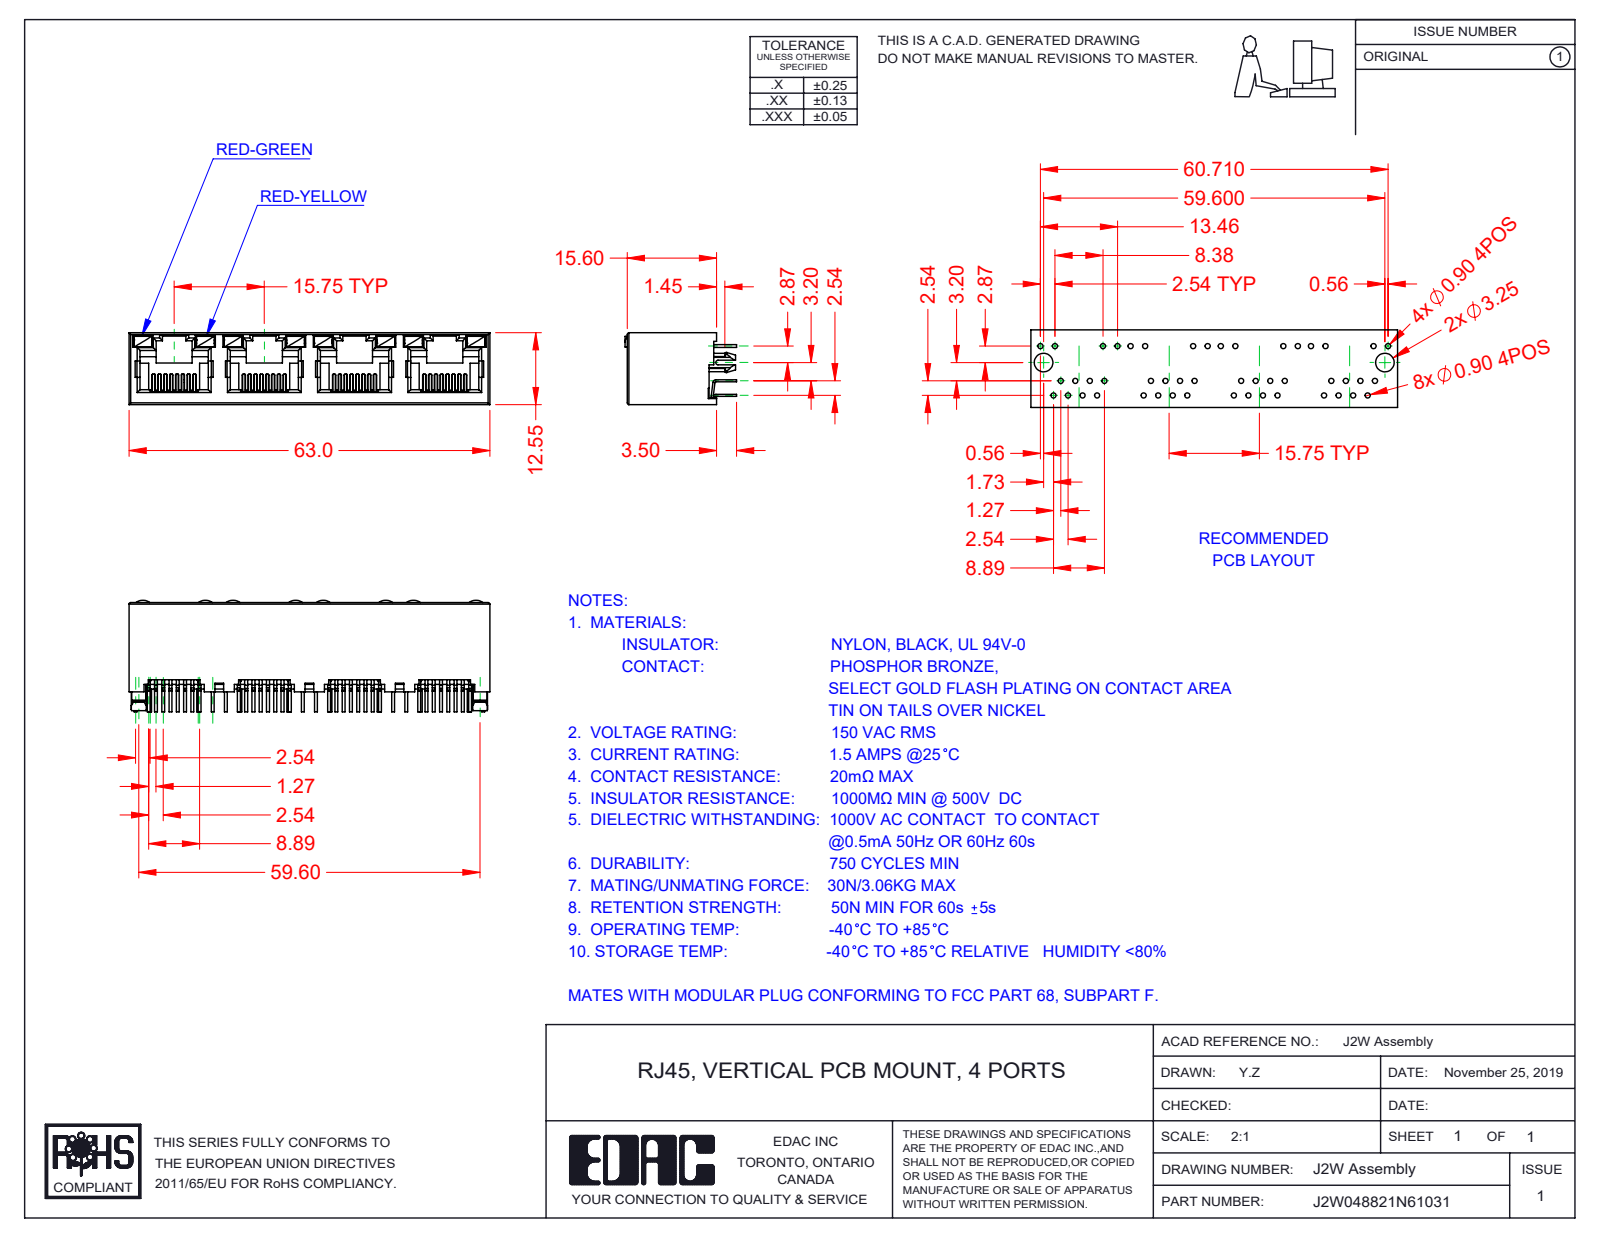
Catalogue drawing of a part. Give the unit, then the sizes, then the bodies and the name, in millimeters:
Units: millimetres
Overall size (bounding box): 63 × 19.5 × 12.55
Partial cylindrical surfaces — rounded edges, fillets, slot ends (radius × count): R0.15 ×64, R0.2 ×29, R0.5 ×28, R0.3 ×14, R0.45 ×8, R2 ×8, R0.25 ×2, R1.5 ×2
Main face-to-face distances: 12.55, 11.9, 0.65, 15.75, 0.36, 1.5, 0.78, 0.6, 11.3, 31.5
Volume: 5 335 mm³ · Surface area: 13 144 mm²
Bodies: 45 solids, 3143 faces (2600 planar, 485 cylindrical, 58 other)
Part name (STEP PRODUCT): 2W Contacts; J2W048821N68131; 2W LED LH_6-Red-Green; 2W LED RH_8-Red-Yellow (+2 more)
STEP written by: SolidWorks 2016 (CONFIG_CONTROL_DESIGN)
